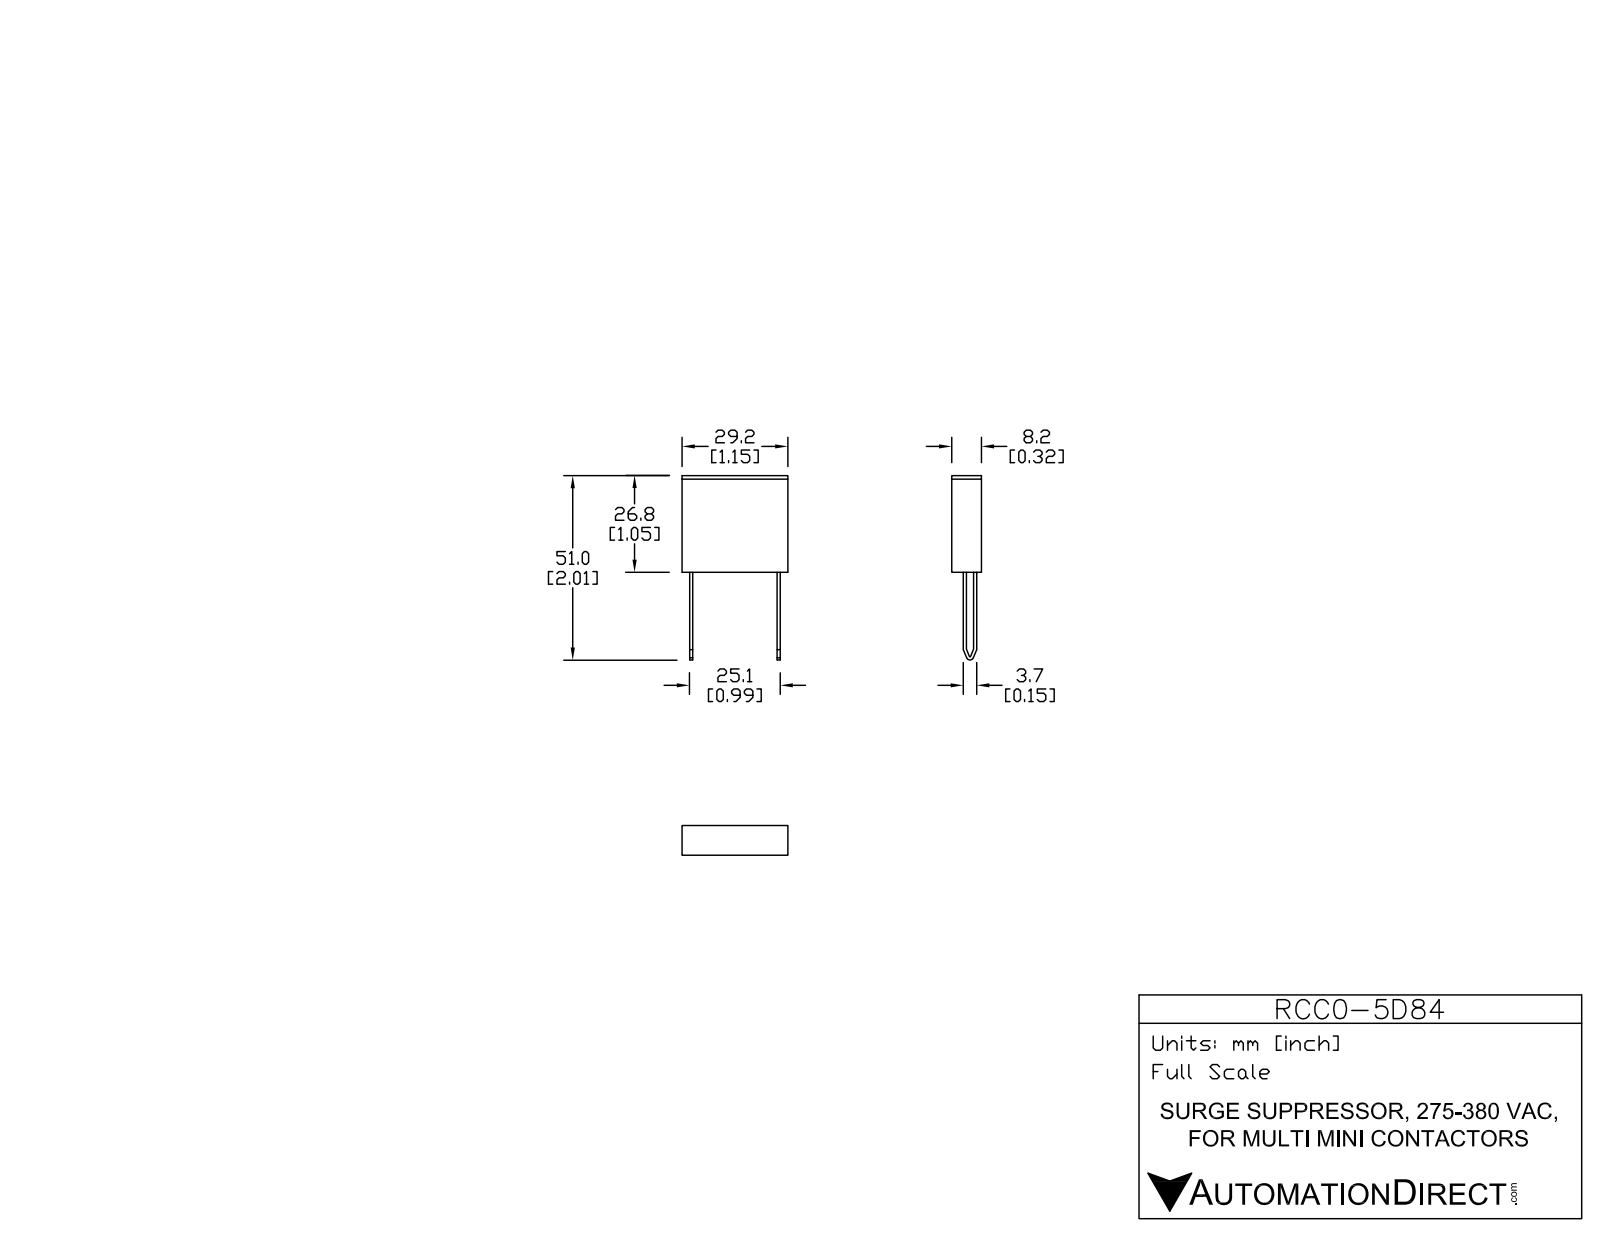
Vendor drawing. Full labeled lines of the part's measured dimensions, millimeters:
Part name (STEP PRODUCT): RCC0-5D84
STEP written by: SolidWorks 2013 (AUTOMOTIVE_DESIGN)
Units: millimetres
Bodies: 1 solid, 34 faces (26 planar, 8 cylindrical, 0 other)
Overall size (bounding box): 50.9 × 29.2 × 8.2
Volume: 6 463 mm³ · Surface area: 2 803 mm²
Partial cylindrical surfaces — rounded edges, fillets, slot ends (radius × count): R0.15 ×1, R1 ×1
Main face-to-face distances: 8.2, 26.7, 29.2, 0.85, 2.1, 27.1, 2.95, 26.25, 24.15, 2.85
